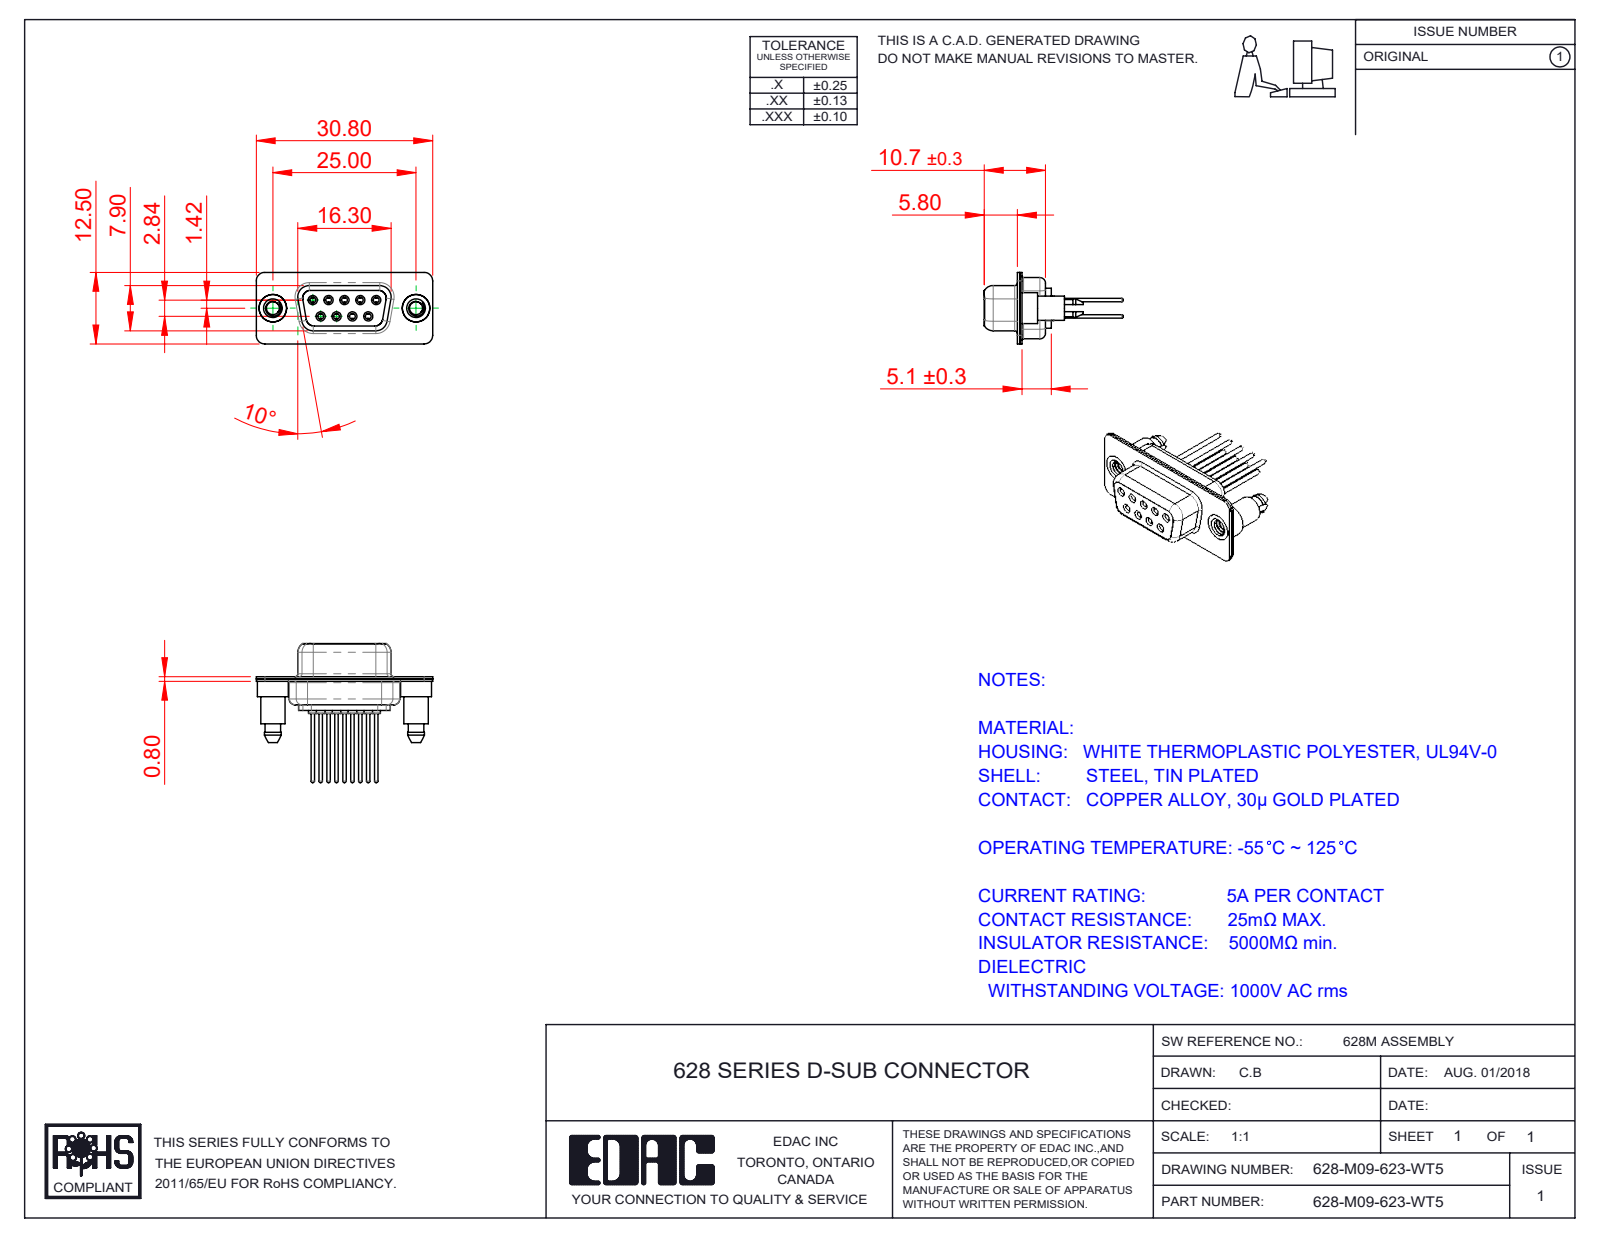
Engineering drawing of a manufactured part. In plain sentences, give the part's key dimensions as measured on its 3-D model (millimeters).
The part is named "628M Contact Row 1_23; 628-M09-623-WT5; 628M Shell Front_09 Contacts; 628M Housing_09 Contacts (+3 more)". Its 3-D file was written by "SolidWorks 2020 (CONFIG_CONTROL_DESIGN)". It is 14 solids with 824 faces: 218 planar, 340 cylindrical and 266 other. Overall it measures 30.8 by 24.27 by 12.5 millimeters. Its volume is 1 853 cubic millimeters and its surface area 4 869 square millimeters. Round holes: 9 of diameter 1, 9 of diameter 1.1, 9 of diameter 1.7, 9 of diameter 1.8, 9 of diameter 2, 2 of diameter 2.26, 2 of diameter 4, 2 of diameter 4.8. Round bosses or shafts: 9 of diameter 2.2, 9 of diameter 1.6, 9 of diameter 1.5, 9 of diameter 0.6, 2 of diameter 5.4, 2 of diameter 4.9, 2 of diameter 4.25. Partial cylindrical surfaces (rounded edges, fillets, slot ends): 18 of radius 1.5, 12 of radius 2, 10 of radius 1.6, 8 of radius 1.35, 4 of radius 0.25, 4 of radius 0.5, 4 of radius 0.6, 4 of radius 0.65. The main face-to-face distances are 0.4, 1.4, 0.45, 8.45, 0.8, 1.8, 1, 8.9, 6.2, 7.05. The hole center spacings are 3.16, 2.77, 5.54, 5.03, 5.04, 8.31, 7.1, 7.48.
